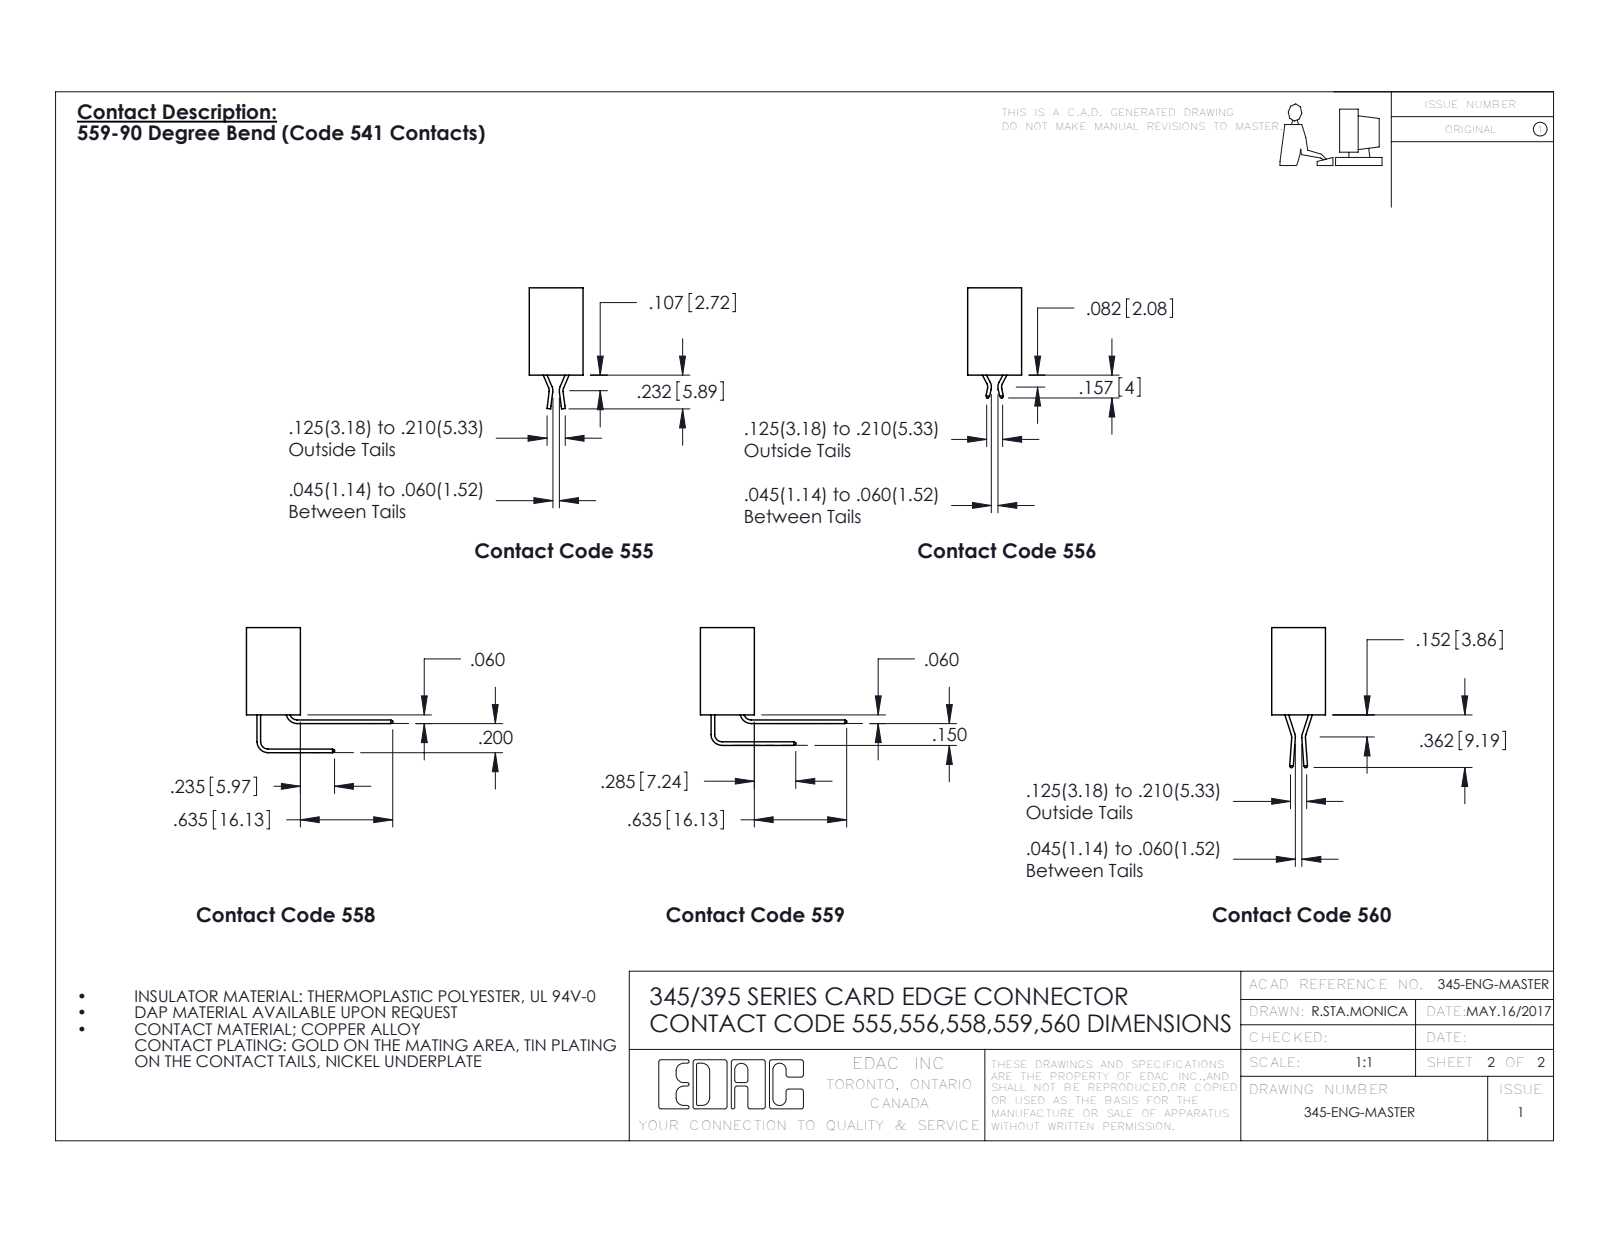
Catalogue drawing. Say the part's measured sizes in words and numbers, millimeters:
The part is named "345-220-058_345-220-058; 345-292-001_555 Tail; 345-250-001_345-250-001-102; 345 Part_0.110 Offset - 0.156 Dia-TH (+1 more)". Its 3-D file was written by "SolidWorks 2016 (CONFIG_CONTROL_DESIGN)". It is 15 solids with 946 faces: 542 planar, 344 cylindrical and 60 other. Overall it measures 84.9 by 47.7 by 9.4 millimeters. Its volume is 12 700 cubic millimeters and its surface area 10 810 square millimeters. Round holes: 2 of diameter 2.3, 2 of diameter 3.2, 2 of diameter 4, 1 of diameter 1.6. Round bosses or shafts: 2 of diameter 3.9. Partial cylindrical surfaces (rounded edges, fillets, slot ends): 25 of radius 0.4, 22 of radius 0.3, 20 of radius 0.5, 16 of radius 1.5, 15 of radius 0.2, 6 of radius 0.2, 6 of radius 0.8, 3 of radius 0.7. The main face-to-face distances are 9.4, 3.8, 5.6, 1.8, 32.9, 3.8, 2, 1.8, 7.6, 7.4. The hole center spacings are 6.9, 21.5, 27.3.
